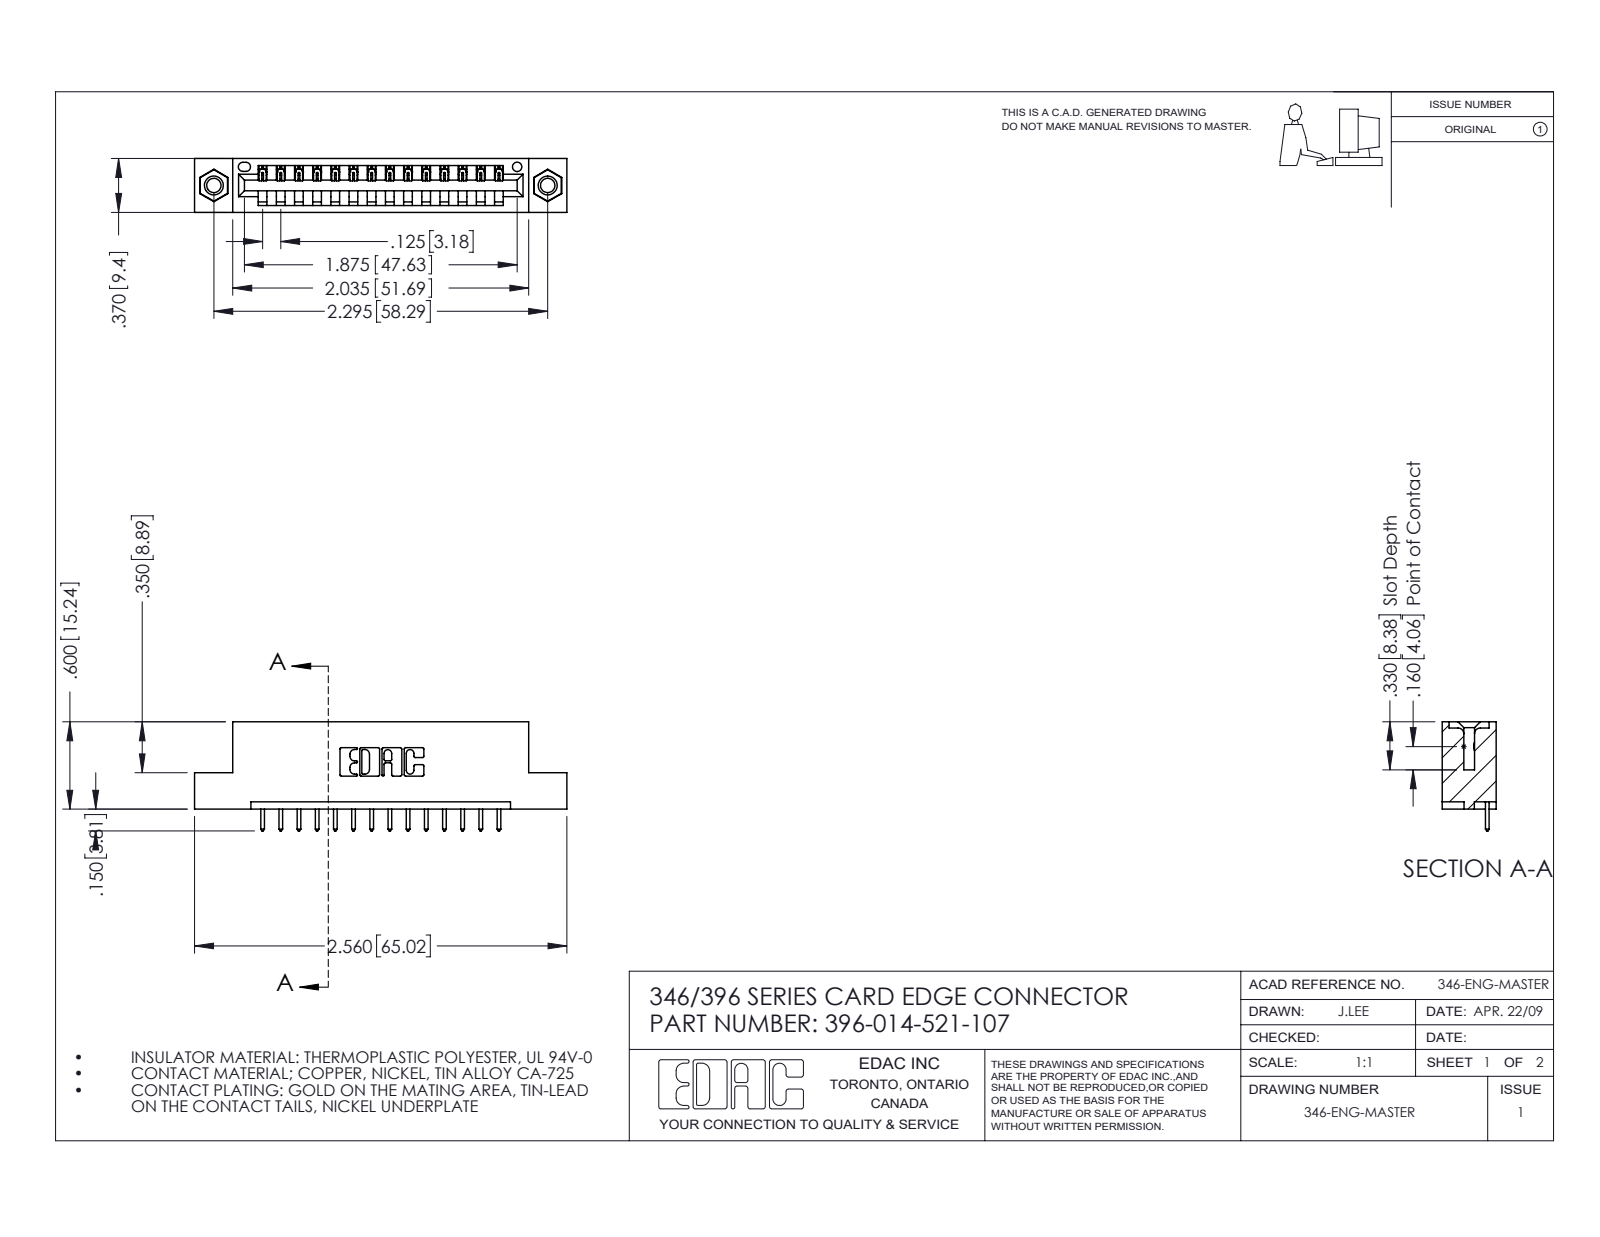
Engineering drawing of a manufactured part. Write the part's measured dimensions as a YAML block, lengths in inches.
part_name: "345-250-001_345-250-005-103; 345-292-001_345-293-121; 396-014-521-107; 346 Part_Flush Mounting Lugs - 0.156 Dia-TI"
step_written_by: "SolidWorks 2016 (CONFIG_CONTROL_DESIGN)"
units: inches
bodies: {solids: 17, faces: 994, planar: 668, cylindrical: 310, other: 16}
overall_size: [2.56, 0.75, 0.37]
volume: 0.365
surface_area: 10.92
round_holes:
  - {diameter: 0.098, count: 2}
  - {diameter: 0.125, count: 2}
  - {diameter: 0.156, count: 2}
  - {diameter: 0.064, count: 1}
round_bosses_or_shafts:
  - {diameter: 0.155, count: 2}
partial_cylinders:
  - {radius: 0.006, count: 28}
  - {radius: 0.01, count: 28}
  - {radius: 0.01, count: 22}
  - {radius: 0.007, count: 6}
  - {radius: 0.031, count: 6}
  - {radius: 0.026, count: 3}
  - {radius: 0.031, count: 2}
  - {radius: 0.04, count: 2}
face_to_face_distances: [0.25, 0.048, 0.322, 0.37, 0.072, 0.298, 0.025, 0.148, 0.222, 0.1]
hole_center_spacings: [0.246, 2.089, 2.295]
